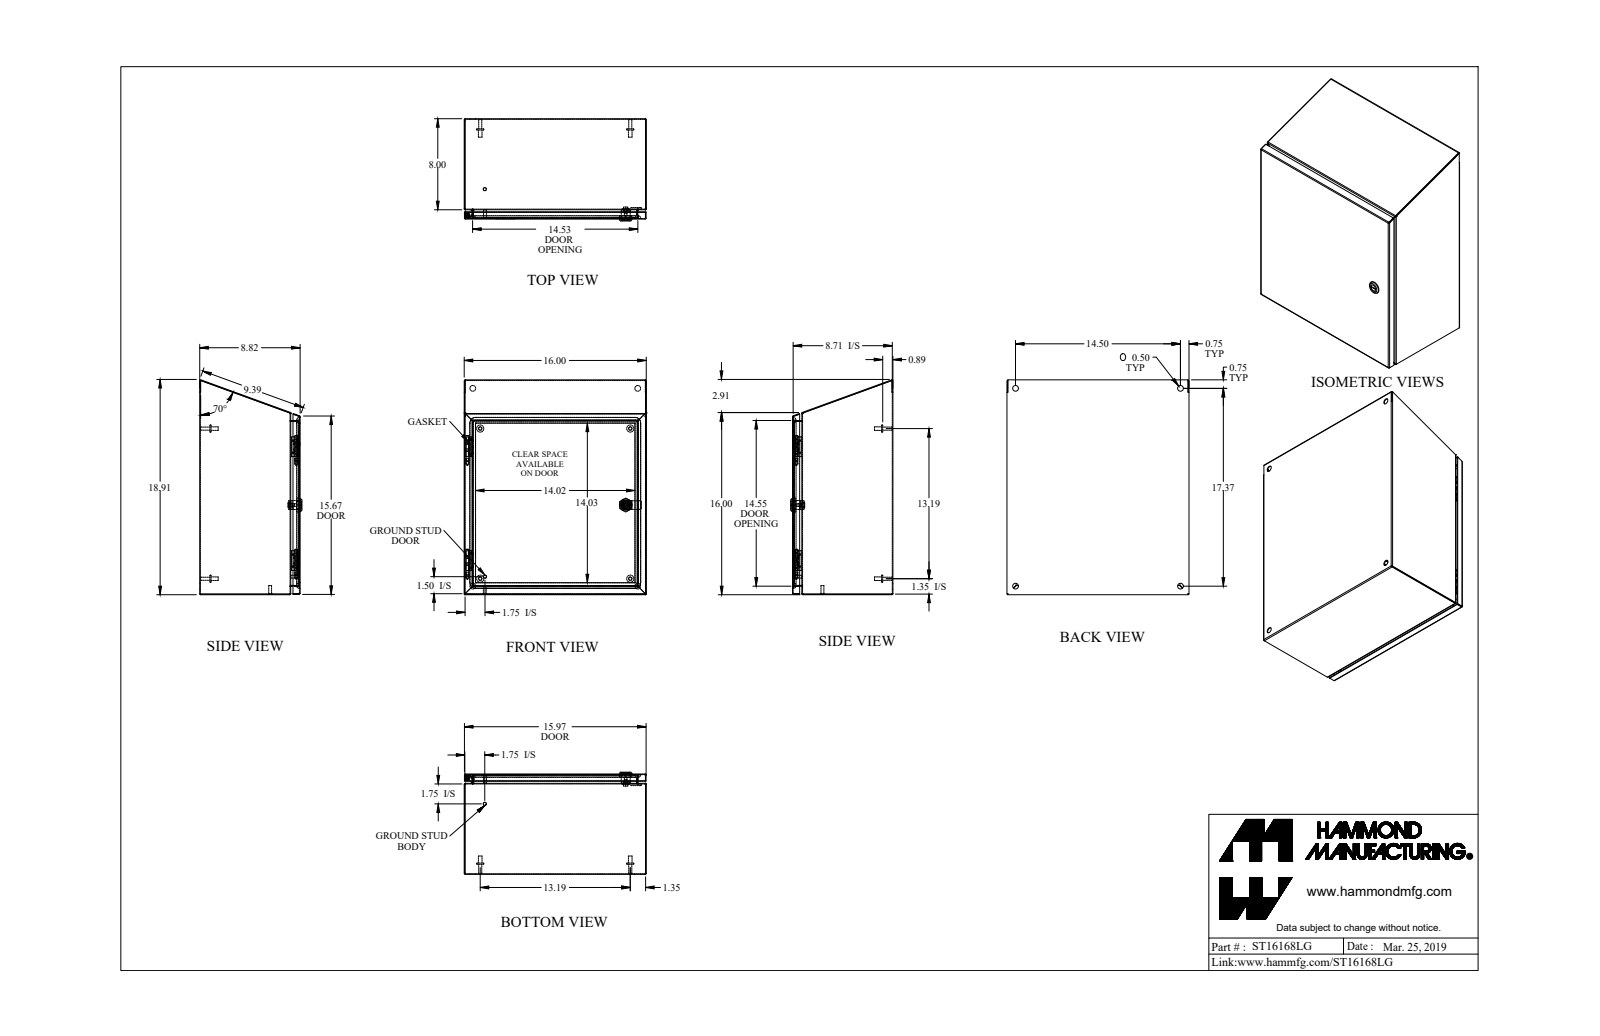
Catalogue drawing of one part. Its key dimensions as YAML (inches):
part_name: "ST16168LG"
step_written_by: "SolidWorks 2018 (AUTOMOTIVE_DESIGN)"
units: inches
bodies: {solids: 21, faces: 632, planar: 303, cylindrical: 197, other: 132}
overall_size: [18.875, 16, 8.982]
volume: 76
surface_area: 2585
round_holes:
  - {diameter: 0.5, count: 4}
  - {diameter: 0.172, count: 1}
  - {diameter: 0.232, count: 1}
  - {diameter: 0.24, count: 1}
  - {diameter: 0.242, count: 1}
  - {diameter: 0.625, count: 1}
  - {diameter: 0.785, count: 1}
round_bosses_or_shafts:
  - {diameter: 0.625, count: 4}
  - {diameter: 0.313, count: 4}
  - {diameter: 0.27, count: 4}
  - {diameter: 0.281, count: 2}
  - {diameter: 0.25, count: 2}
  - {diameter: 1.1, count: 1}
  - {diameter: 0.525, count: 1}
  - {diameter: 0.455, count: 1}
partial_cylinders:
  - {radius: 0.029, count: 21}
  - {radius: 0.086, count: 21}
  - {radius: 0.25, count: 11}
  - {radius: 0.006, count: 4}
  - {radius: 0.062, count: 4}
  - {radius: 0.499, count: 4}
  - {radius: 0.125, count: 2}
  - {radius: 0.021, count: 1}
face_to_face_distances: [0.057, 0.057, 8.765, 8.708, 15.943, 8.822, 8.765, 15.886, 16, 0.822]
hole_center_spacings: [14.5, 17.374, 22.63, 7.206, 10.302, 15.214, 16.902]
